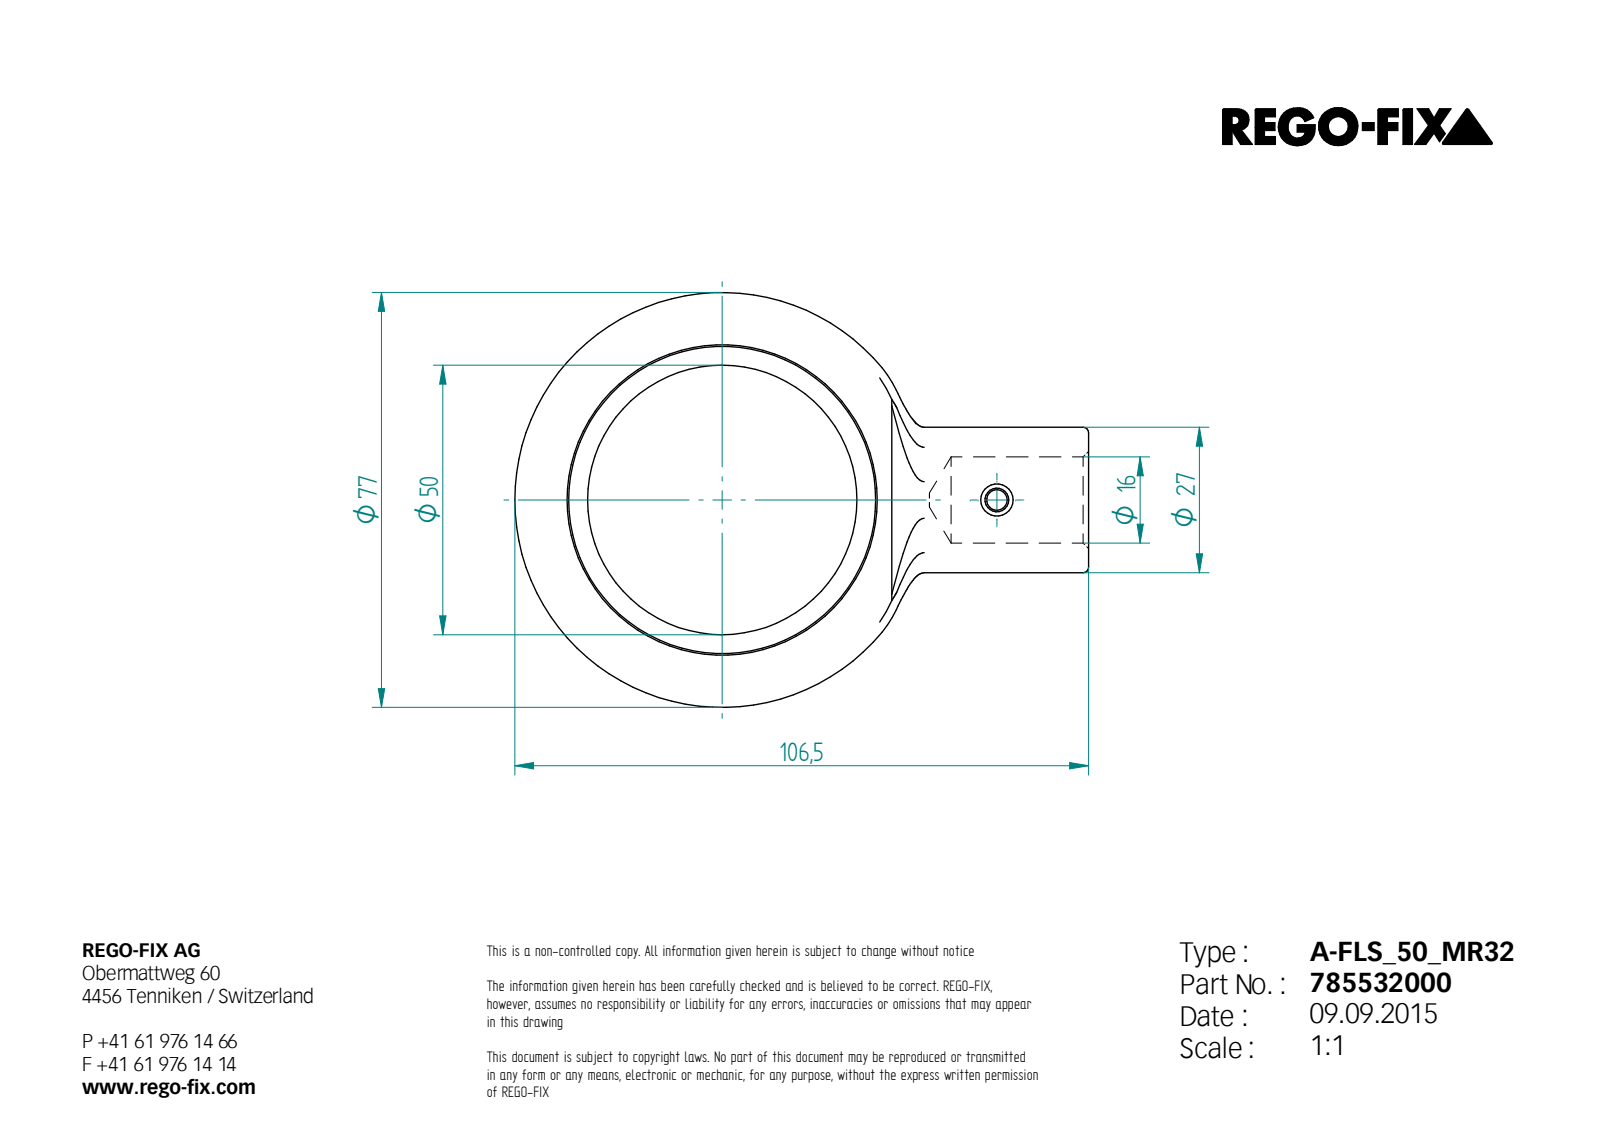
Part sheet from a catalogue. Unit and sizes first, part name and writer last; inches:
Units: inches
Overall size (bounding box): 4.193 × 3.031 × 1.18
Round holes (diameter × count): ⌀0.177 ×1, ⌀0.217 ×1, ⌀0.63 ×1, ⌀1.969 ×1, ⌀2.244 ×1
Round bosses / shafts (diameter × count): ⌀1.063 ×1, ⌀0.205 ×1, ⌀0.173 ×1, ⌀0.138 ×1
Partial cylindrical surfaces — rounded edges, fillets, slot ends (radius × count): R0.157 ×1, R1.049 ×1, R1.061 ×1
Main face-to-face distances: 1.024, 0.118, 1.142, 0.098, 0.02, 1.043, 0.039, 0.059, 0.079, 1.102
Hole centre spacings: 2.008
Volume: 4.748 in³ · Surface area: 43.45 in²
Bodies: 4 solids, 132 faces (73 planar, 15 cylindrical, 44 other)
Part name (STEP PRODUCT): 0006487; 0006879; 0006880; 0006994
STEP written by: Unknown (AUTOMOTIVE_DESIGN)
